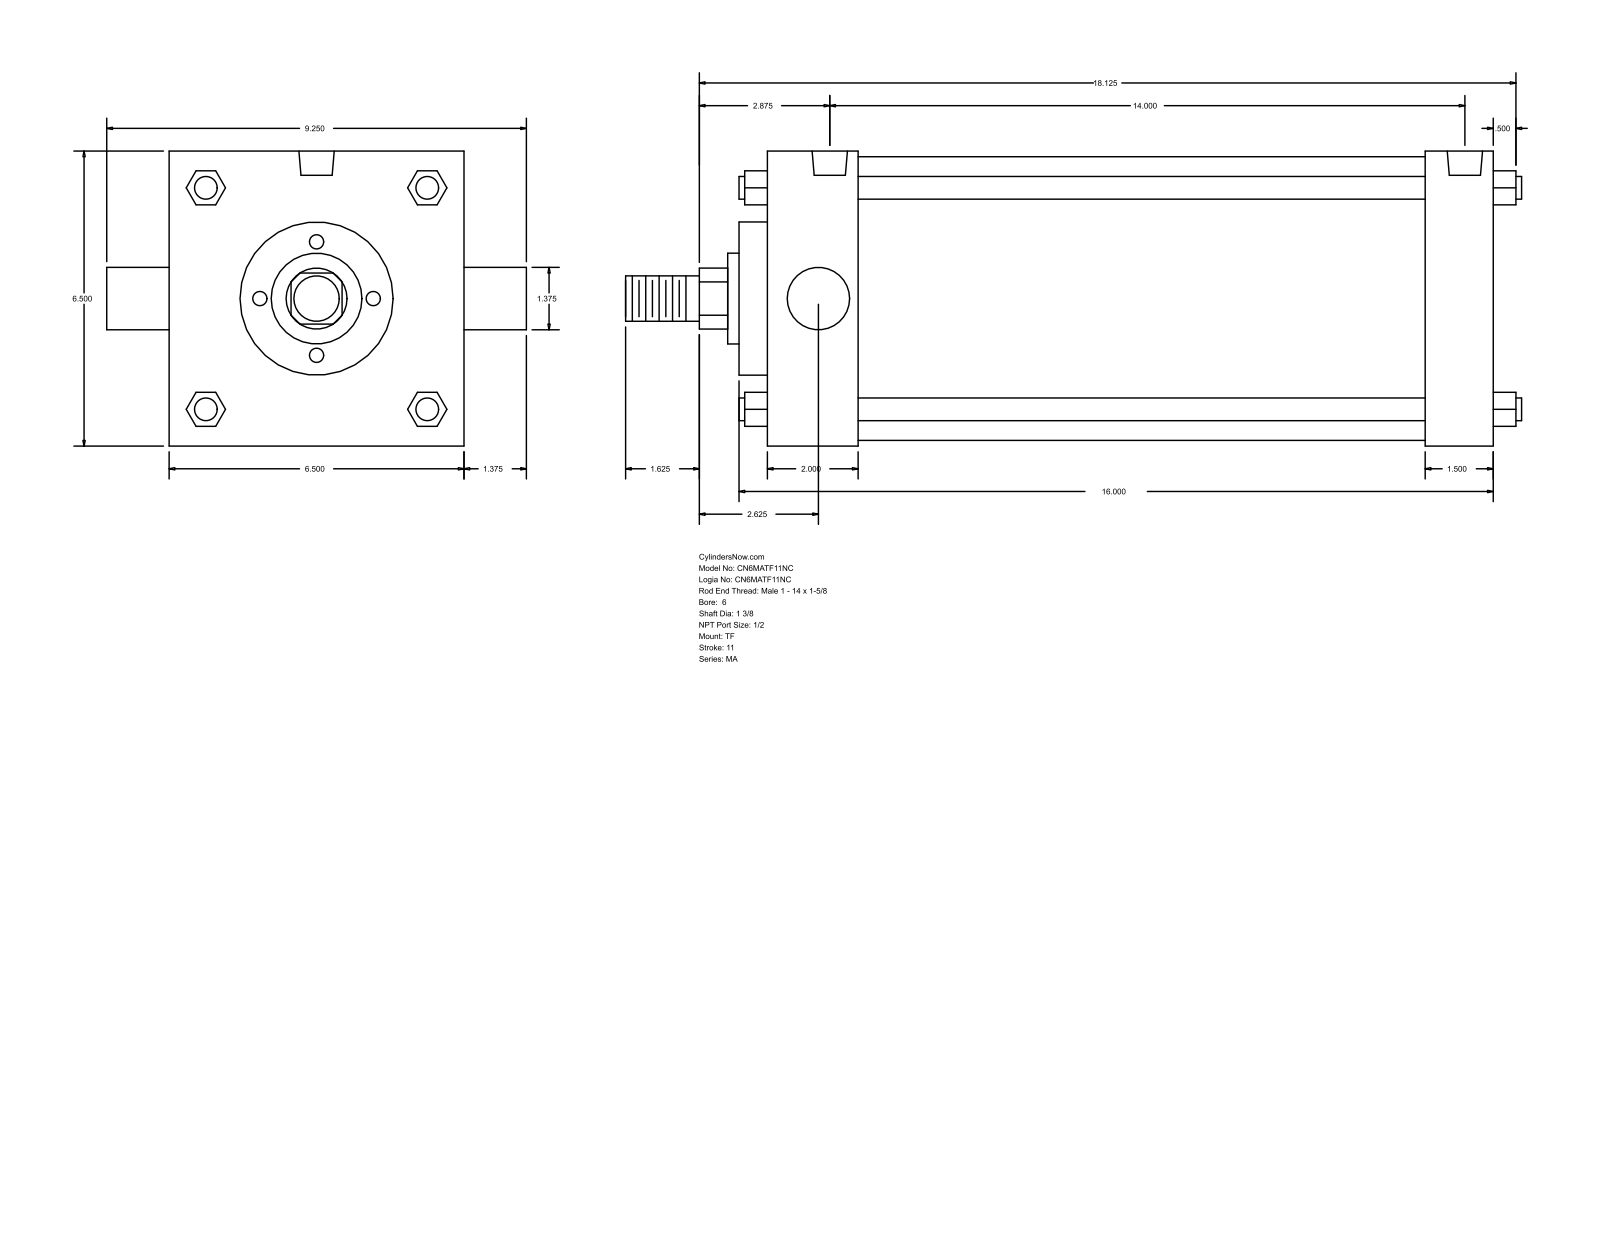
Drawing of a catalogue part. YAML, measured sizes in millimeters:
part_name: "MA_TF__0600_1.375"
step_written_by: "GSSL Pune (CONFIG_CONTROL_DESIGN)"
units: millimeters
bodies: {solids: 0, faces: 122, planar: 93, cylindrical: 29, other: 0}
overall_size: [501.65, 234.95, 165.1]
round_holes:
  - {diameter: 17.46, count: 3}
  - {diameter: 19.77, count: 2}
round_bosses_or_shafts:
  - {diameter: 12.7, count: 4}
  - {diameter: 34.92, count: 2}
  - {diameter: 158.75, count: 1}
  - {diameter: 85.72, count: 1}
  - {diameter: 50.8, count: 1}
  - {diameter: 25.4, count: 1}
partial_cylinders:
  - {radius: 17.06, count: 1}
face_to_face_distances: [165.1, 409.58, 50.8, 358.78, 371.47, 320.67, 38.11, 66.67, 15.87, 387.34]
hole_center_spacings: [3.18, 355.59, 358.77]
